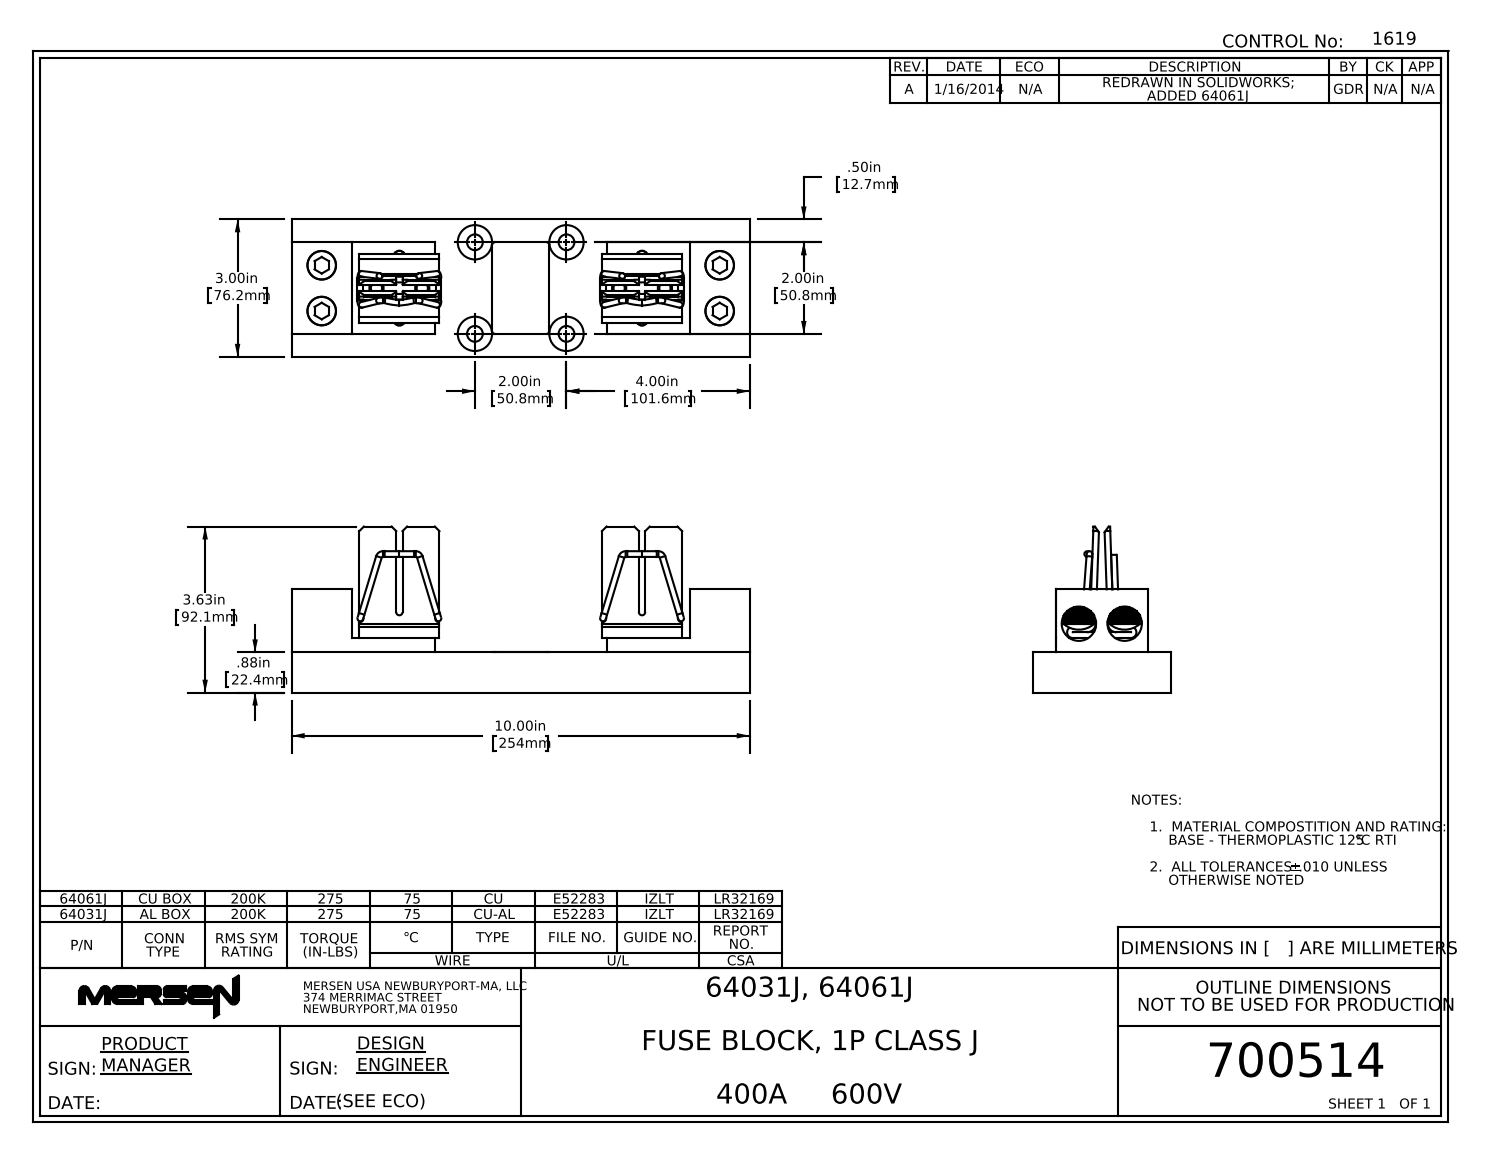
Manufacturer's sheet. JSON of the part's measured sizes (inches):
{"part_name": "700514revA", "step_written_by": "SolidWorks 2013 (AUTOMOTIVE_DESIGN)", "units": "inches", "bodies": {"solids": 20, "faces": 516, "planar": 234, "cylindrical": 82, "other": 200}, "overall_size": [10.004, 3.627, 3], "volume_in3": 34.98, "surface_area_in2": 241.5, "round_holes": [[0.257, 8], [0.625, 7], [0.75, 6], [0.339, 4], [0.344, 4], [0.85, 4], [0.625, 3], [0.316, 2], [0.377, 2]], "round_bosses_or_shafts": [[0.313, 8]], "partial_cylinders_radius": [[0.06, 4], [0.094, 4], [0.063, 2], [0.069, 2], [0.125, 2], [0.187, 2]], "face_to_face_distances": [0.88, 0.124, 0.312, 1.192, 3, 0.5, 0.25, 2, 0.502, 2.502], "hole_center_spacings": [5.3, 1, 0.851, 0.852, 4.849, 5.841, 6.515, 7.513]}
